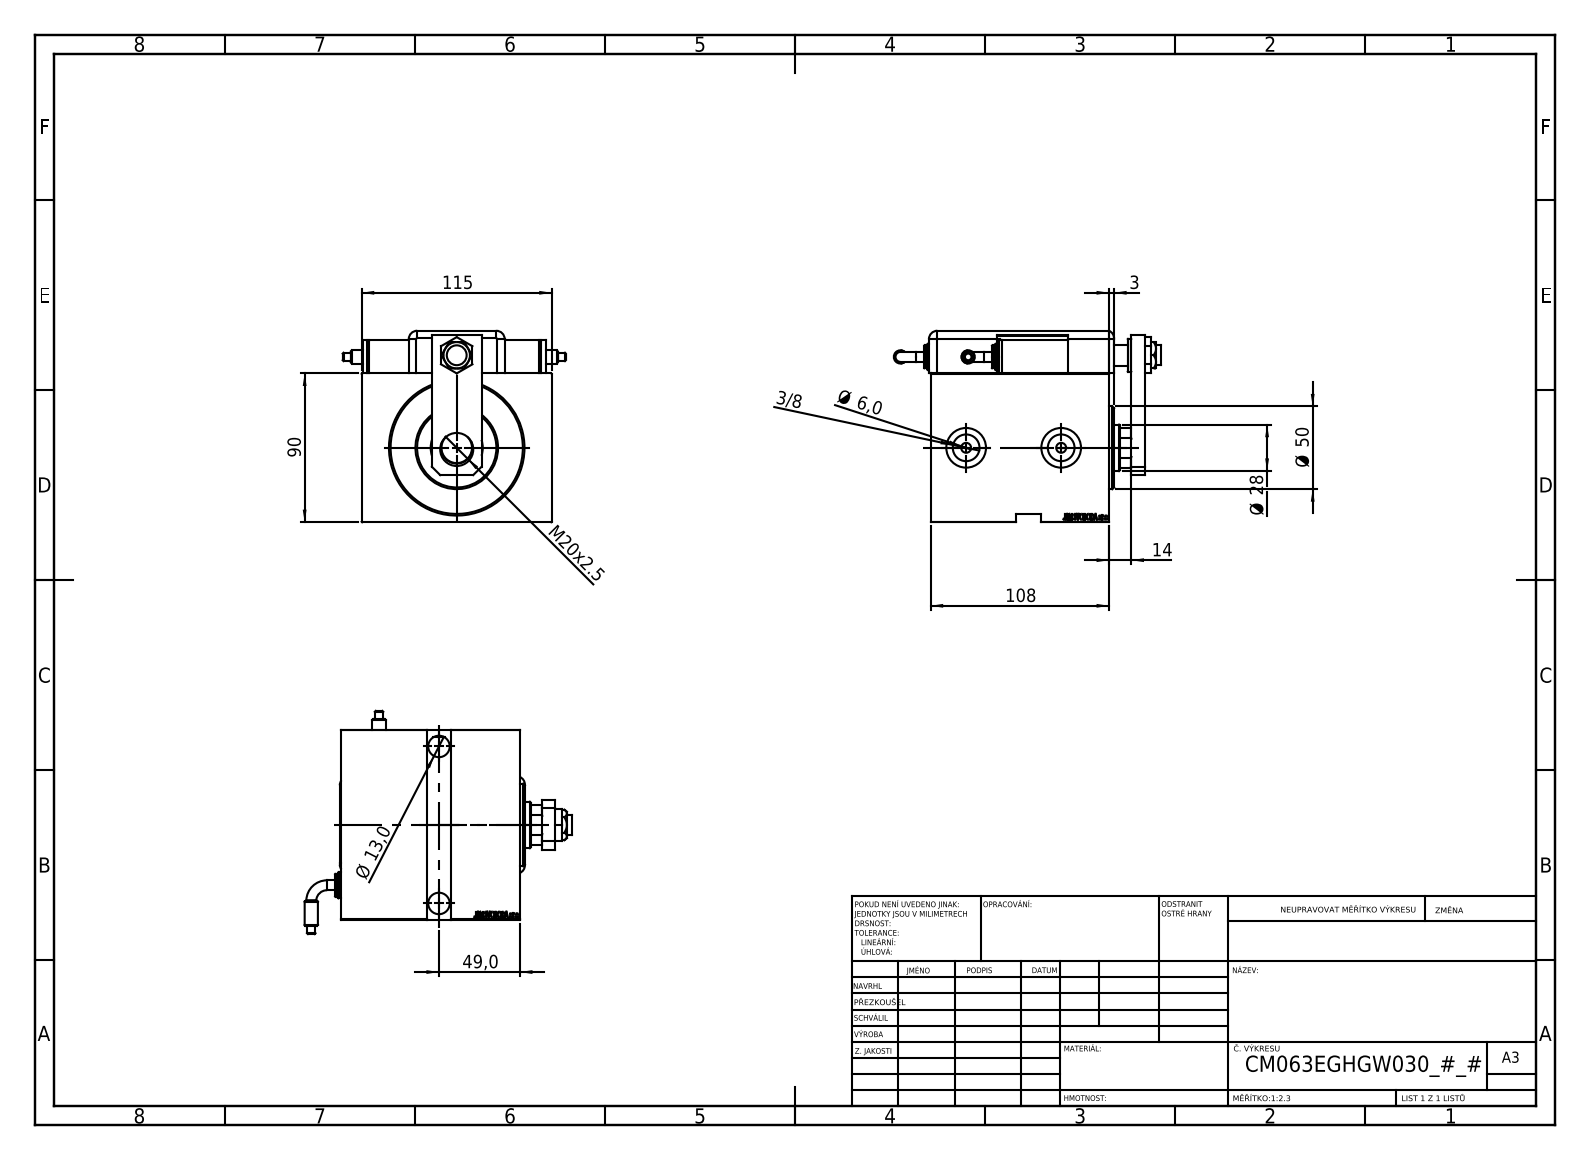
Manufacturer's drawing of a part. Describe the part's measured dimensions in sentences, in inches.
The part is named "TYC; V450CM_VC_B; KRYT; NUT_D13 (+7 more)". Its 3-D file was written by "SolidWorks 2019 (CONFIG_CONTROL_DESIGN)". It is 13 solids with 1258 faces: 618 planar, 107 cylindrical and 533 other. Overall it measures 6.357 by 5.315 by 4.559 inches. Its volume is 70.91 cubic inches and its surface area 291.4 square inches. Round holes: 3 of diameter 0.512, 2 of diameter 0.157, 2 of diameter 0.236, 2 of diameter 0.315, 2 of diameter 0.637, 2 of diameter 0.748, 2 of diameter 0.945, 1 of diameter 0.472, 1 of diameter 0.551, 1 of diameter 0.728, 1 of diameter 0.787, 1 of diameter 1.102. Round bosses or shafts: 3 of diameter 0.787, 2 of diameter 0.63, 2 of diameter 0.551, 2 of diameter 0.315, 2 of diameter 0.236, 2 of diameter 0.198, 1 of diameter 2.559, 1 of diameter 1.969. Partial cylindrical surfaces (rounded edges, fillets, slot ends): 9 of radius 0.197, 1 of radius 0.394, 1 of radius 0.531. The main face-to-face distances are 4.252, 0.118, 3.543, 4.528, 3.563, 0.689, 0.728, 0.197, 4.559, 1.016. The hole center spacings are 2.202, 2.792, 0.039, 0.787, 2.205, 2.244, 2.264, 3.74.
